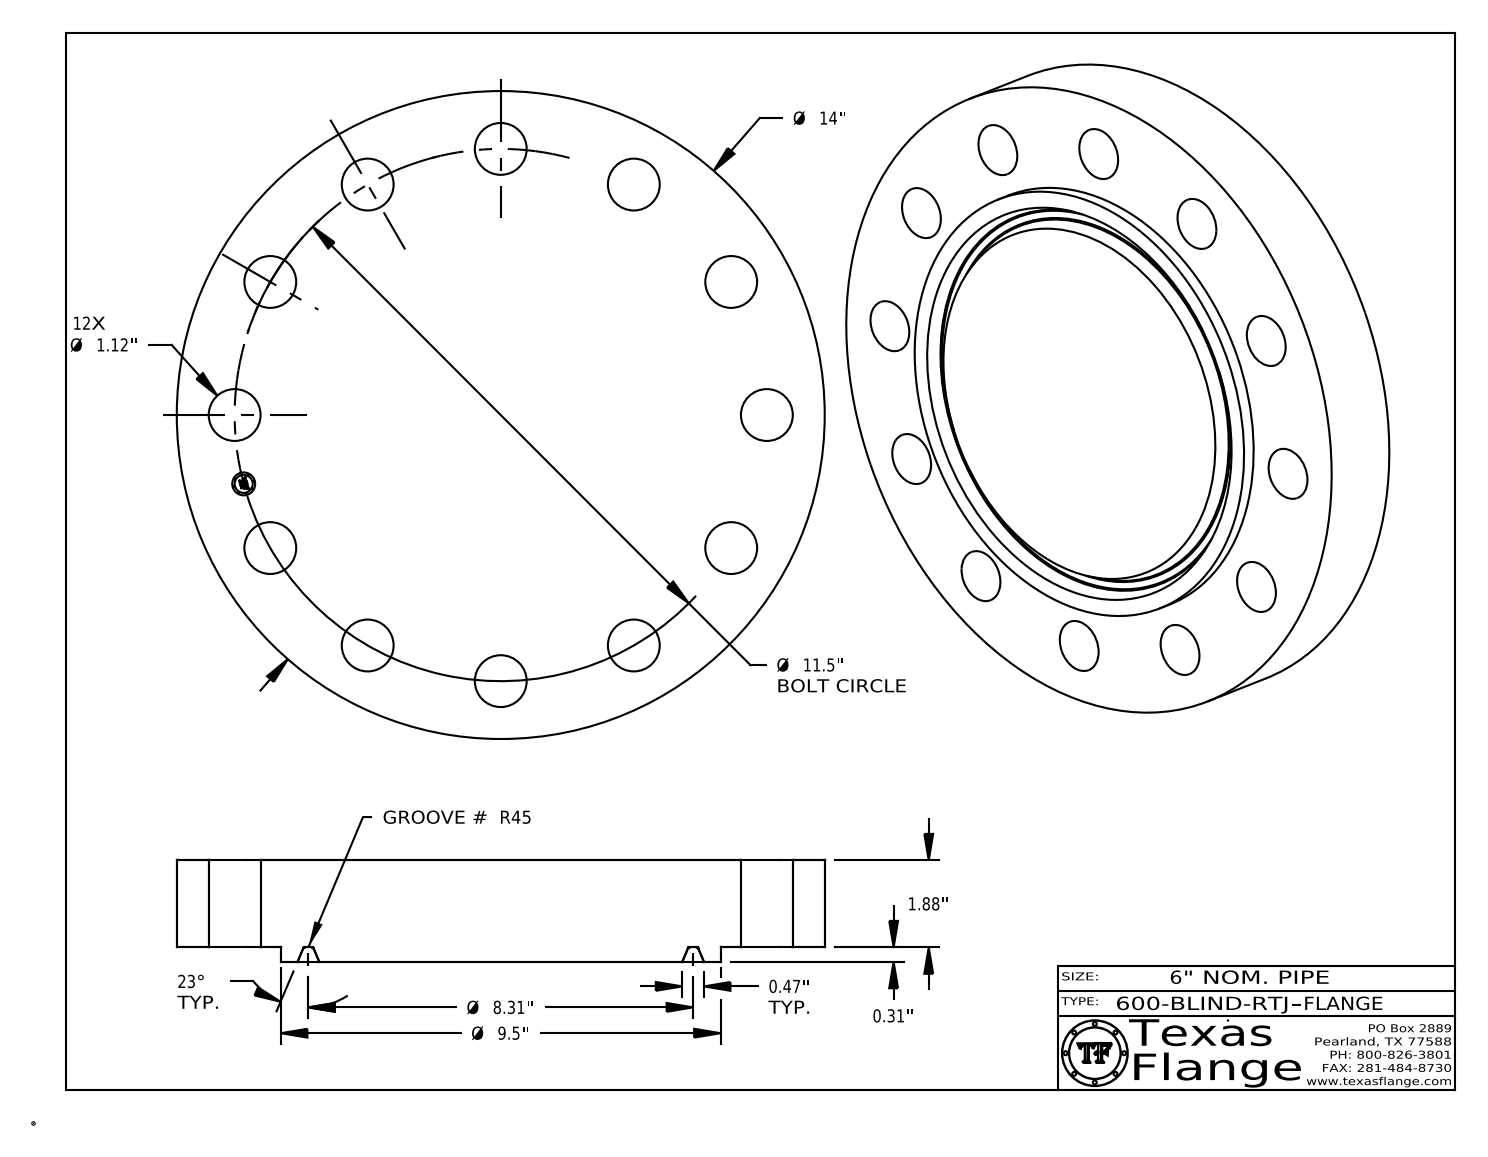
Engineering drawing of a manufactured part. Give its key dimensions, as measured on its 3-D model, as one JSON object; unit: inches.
{"part_name": "600-BLIND-RTJ", "step_written_by": "CATIA V5 STEP AP214 (AUTOMOTIVE_DESIGN)", "units": "inches", "bodies": {"solids": 1, "faces": 426, "planar": 370, "cylindrical": 48, "other": 8}, "overall_size": [14, 14, 2.193], "volume_in3": 286.6, "surface_area_in2": 466.3, "round_holes": [[1.12, 12], [0.495, 1]], "round_bosses_or_shafts": [[0.03, 8], [14, 1], [9.5, 1], [0.39, 1]], "face_to_face_distances": [1.88, 0.313, 2.193, 2.178, 1.865, 0.015, 0.148, 0.144, 0.027, 0.096], "hole_center_spacings": [8.132, 11.108, 2.977, 5.75, 9.959, 11.5, 2.976, 5.75]}
